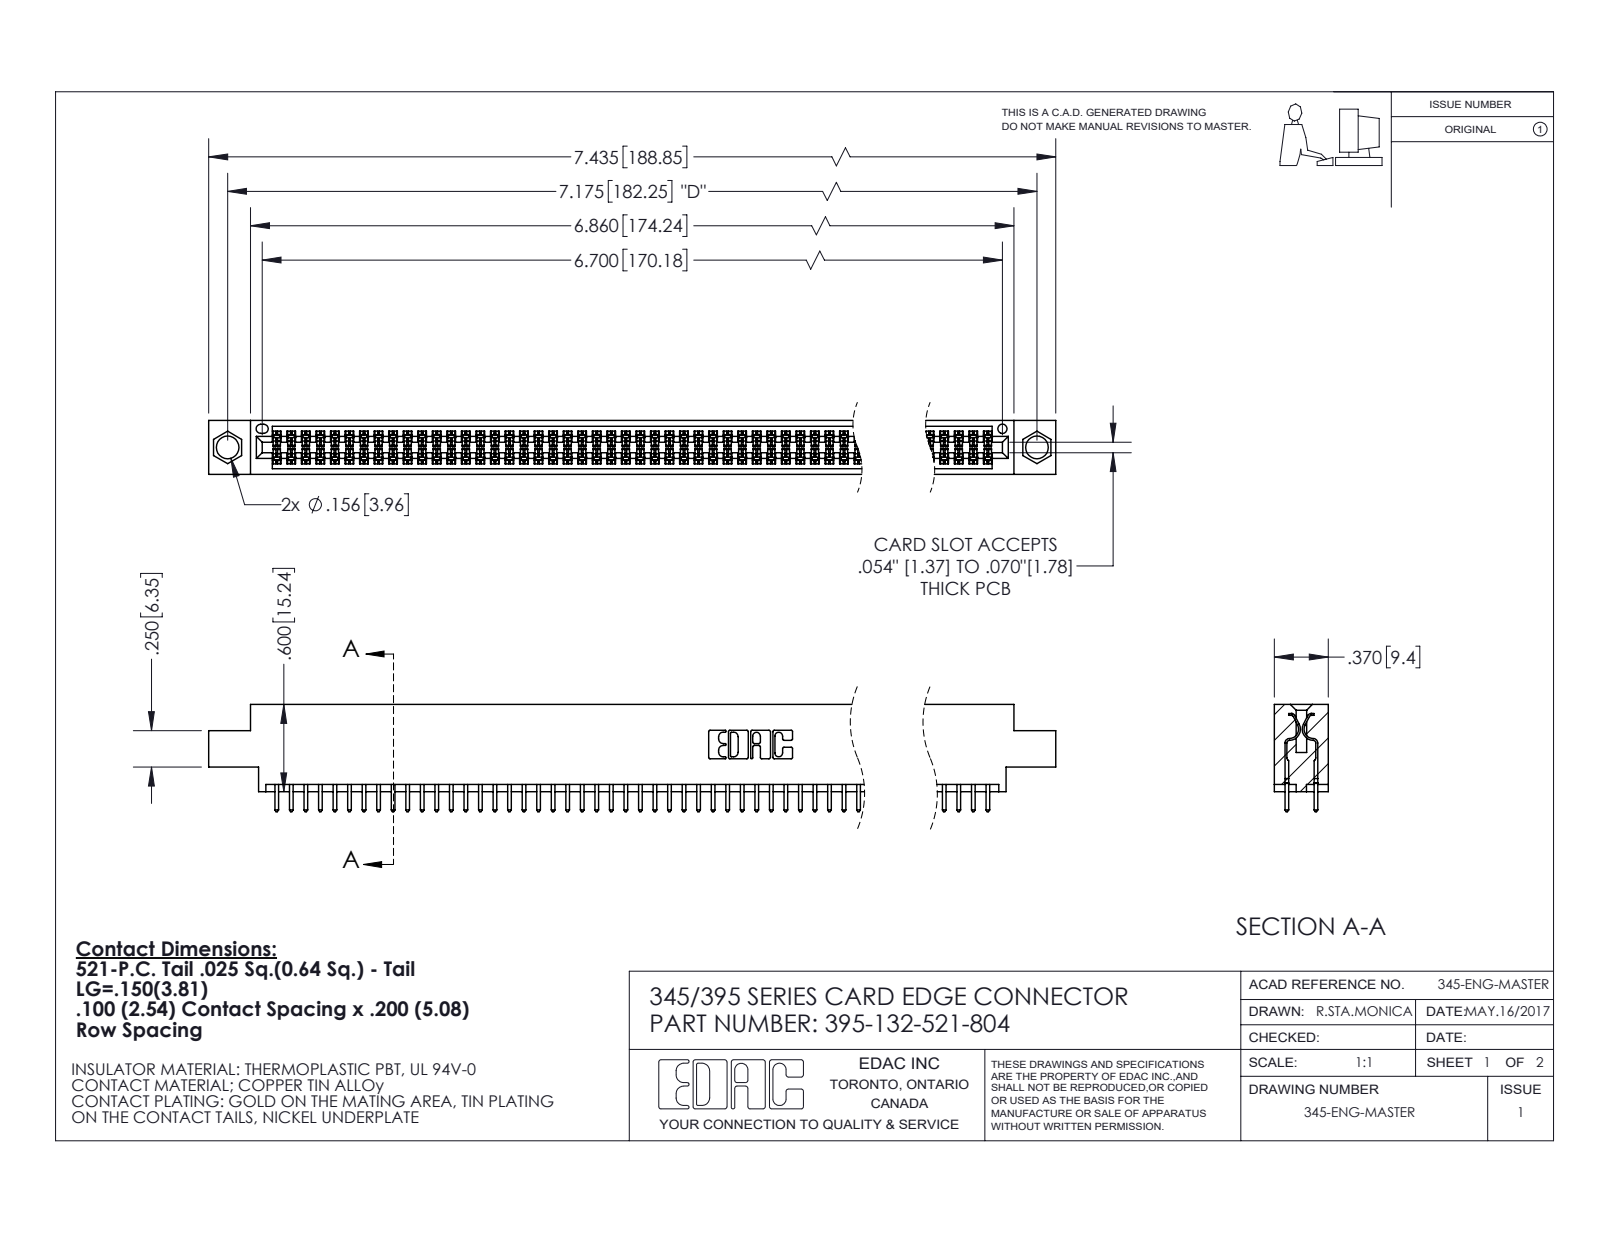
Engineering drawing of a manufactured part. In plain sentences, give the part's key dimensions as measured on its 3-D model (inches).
The part is named "395-132-521-804; 345 Part_0.170 Offset - 0.156 Dia-TI; 345-292-001_345-293-121". Its 3-D file was written by "SolidWorks 2020 (CONFIG_CONTROL_DESIGN)". It is 133 solids with 6744 faces: 4454 planar, 2290 cylindrical and 0 other. Overall it measures 7.435 by 0.737 by 0.37 inches. Its volume is 1.116 cubic inches and its surface area 42.09 square inches. Round holes: 2 of diameter 0.156, 1 of diameter 0.064. Partial cylindrical surfaces (rounded edges, fillets, slot ends): 199 of radius 0.006, 132 of radius 0.01, 22 of radius 0.01, 6 of radius 0.007, 6 of radius 0.031, 3 of radius 0.026, 2 of radius 0.014, 2 of radius 0.019. The main face-to-face distances are 0.072, 0.298, 0.2, 0.37, 0.098, 0.272, 0.025, 0.225, 0.175, 0.149. The hole center spacings are 0.27, 6.939, 7.175.
